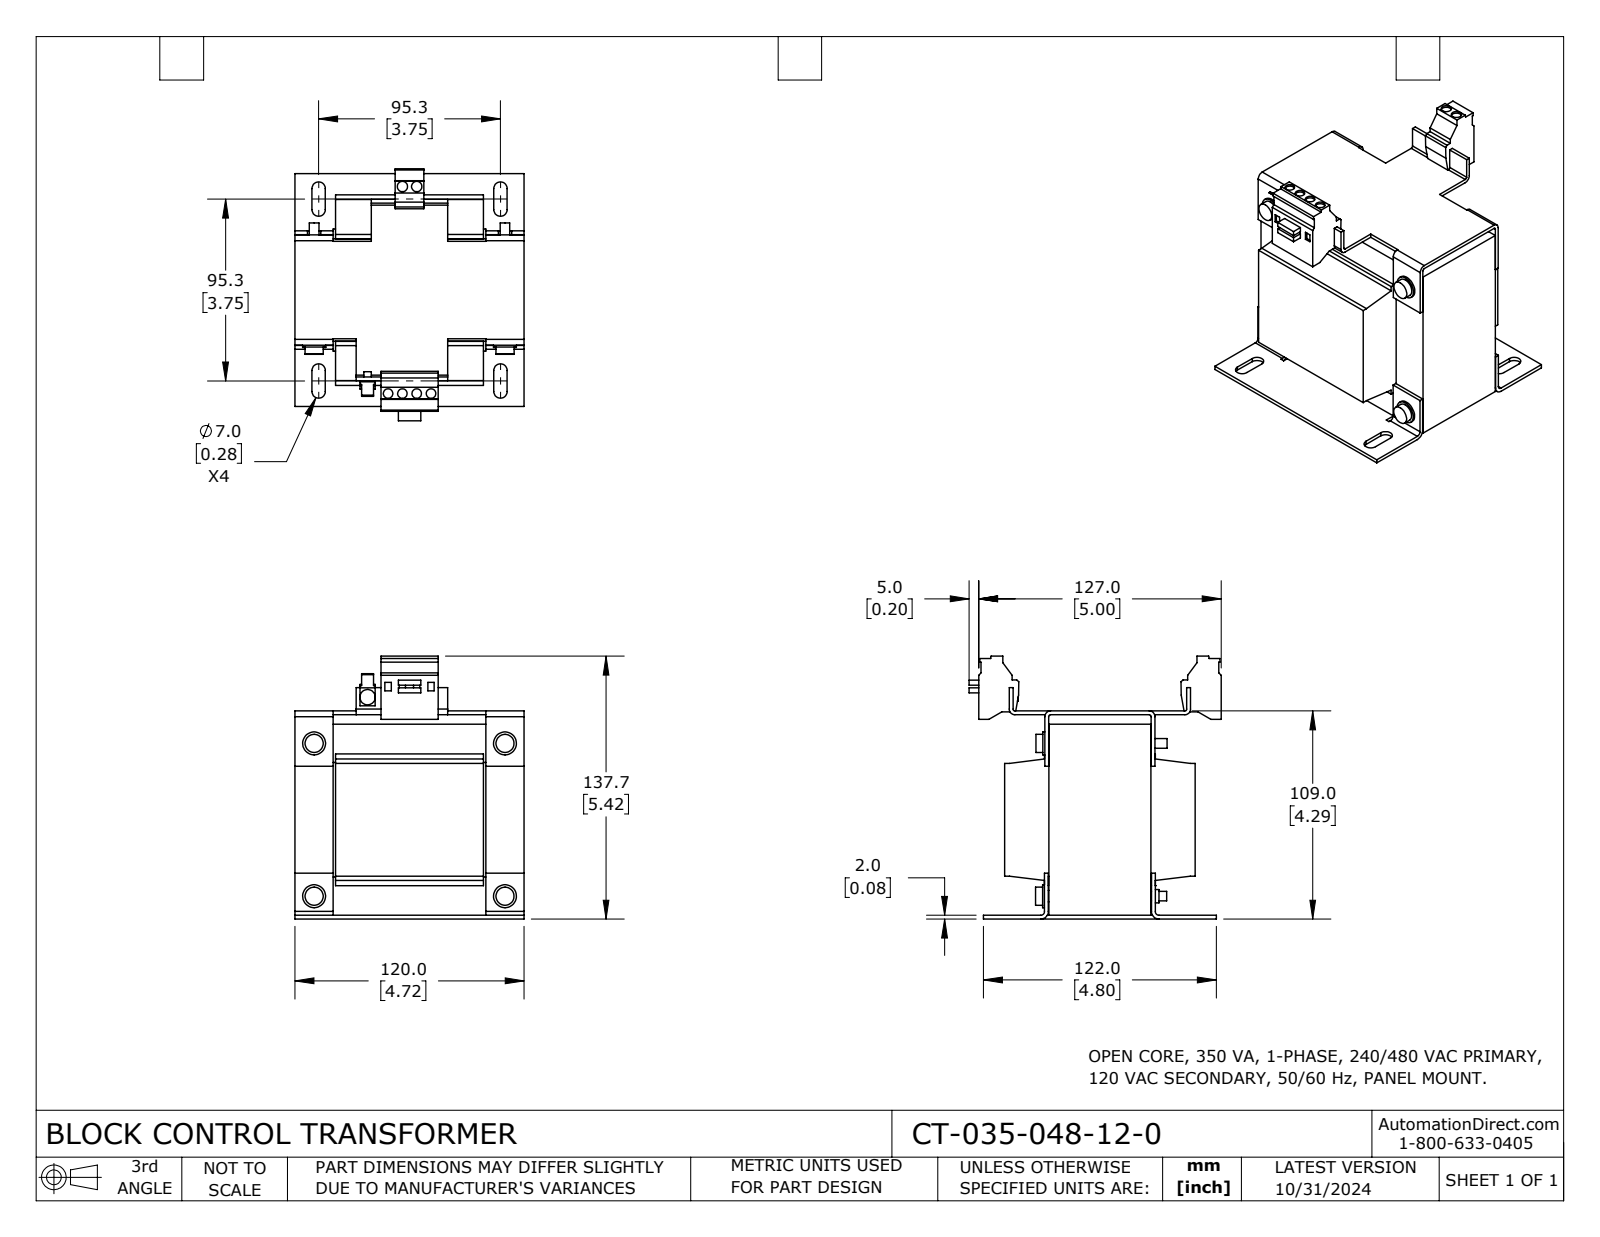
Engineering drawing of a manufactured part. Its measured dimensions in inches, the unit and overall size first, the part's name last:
Units: inches
Overall size (bounding box): 5.421 × 5.197 × 4.724
Round holes (diameter × count): ⌀0.197 ×4, ⌀0.213 ×2
Round bosses / shafts (diameter × count): ⌀0.472 ×4, ⌀0.374 ×4, ⌀0.236 ×4, ⌀0.197 ×4, ⌀0.276 ×2, ⌀0.315 ×1, ⌀0.157 ×1
Partial cylindrical surfaces — rounded edges, fillets, slot ends (radius × count): R0.138 ×8, R0.039 ×4, R0.118 ×4, R0.079 ×2, R0.157 ×2
Main face-to-face distances: 0.079, 4.213, 3.937, 0.837, 3.888, 0.787, 0.911, 3.018, 3.1, 3.15
Hole centre spacings: 0.295, 4.278, 0.591, 4.268, 4.308, 0.886
Volume: 56.7 in³ · Surface area: 209.4 in²
Bodies: 1 solid, 327 faces (235 planar, 92 cylindrical, 0 other)
Part name (STEP PRODUCT): CT-035-048-12-0
STEP written by: SolidWorks 2023 (CONFIG_CONTROL_DESIGN)
